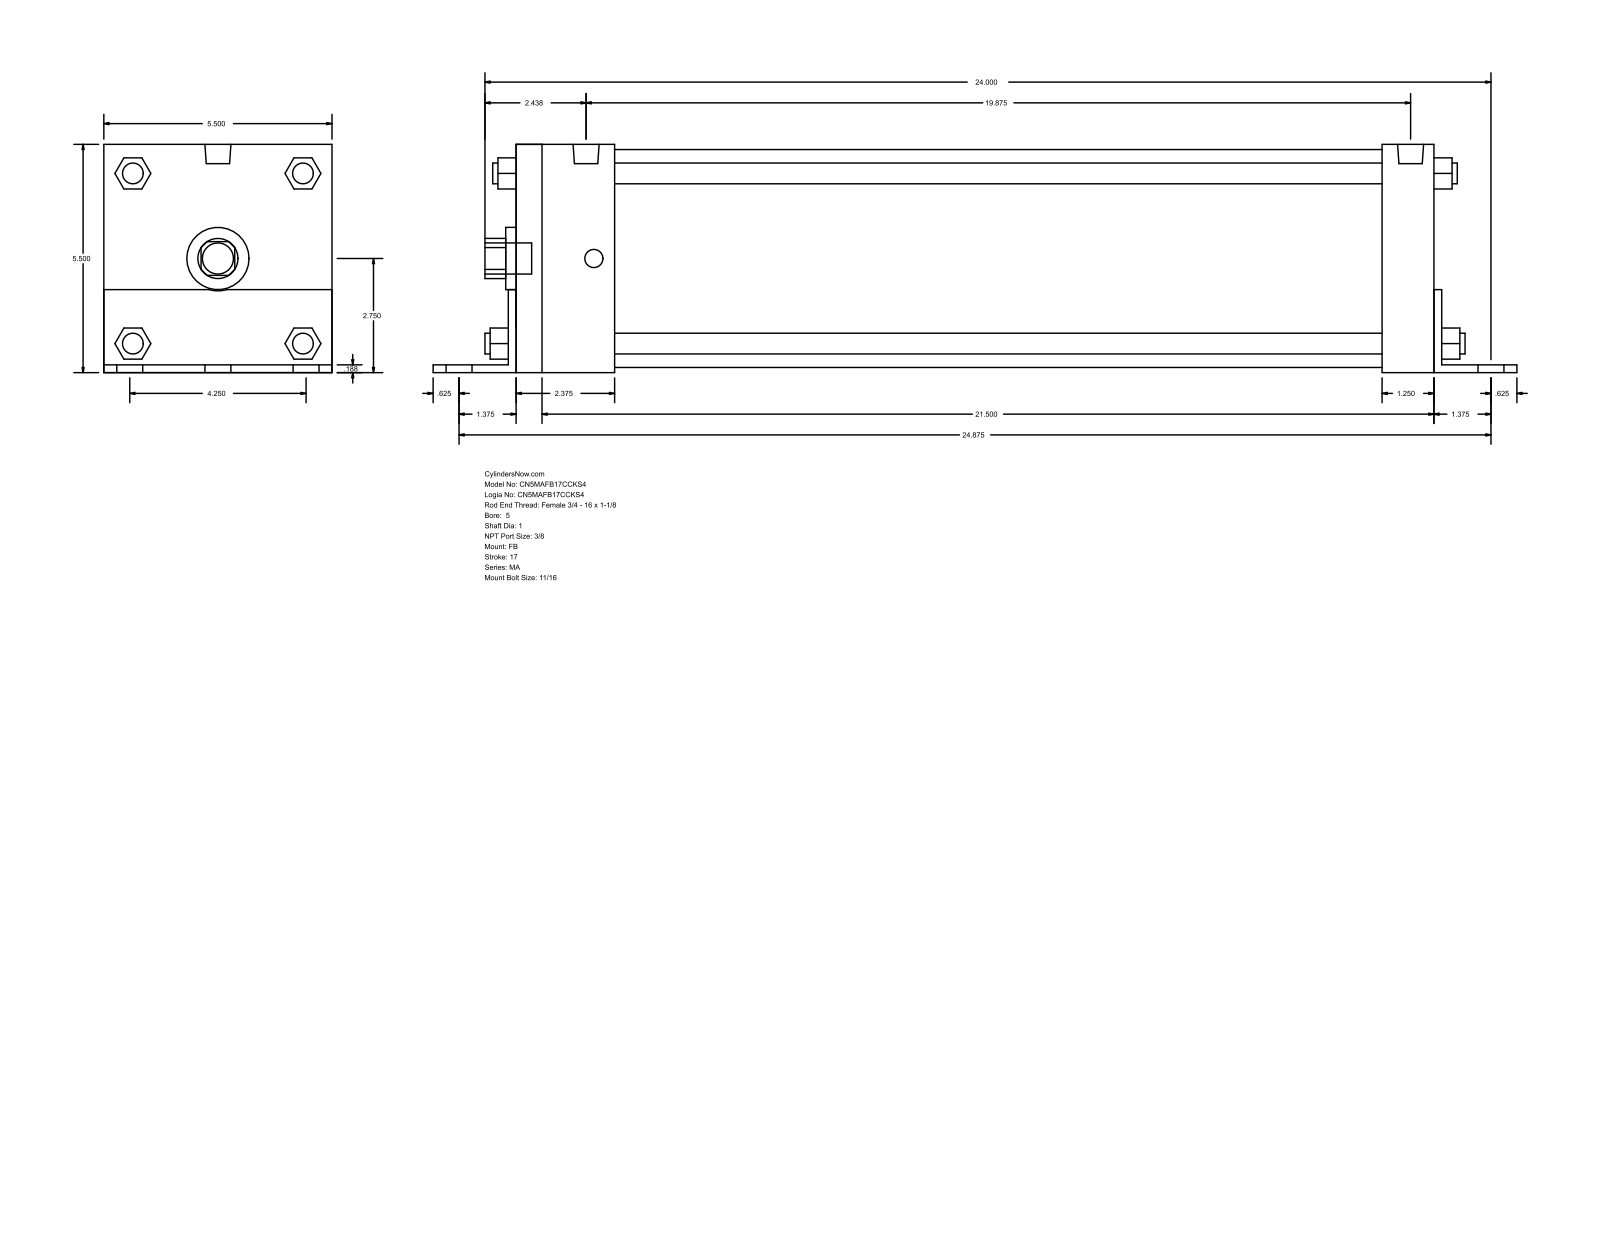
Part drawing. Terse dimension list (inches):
name: MA_FB__0500_1
written by: GSSL Pune (CONFIG_CONTROL_DESIGN)
unit: in
bodies: 0 solids, 140 faces (105 planar, 35 cylindrical, 0 other)
size: 26.125 × 5.502 × 5.5
holes: 1× ⌀1, 1× ⌀1.5, 1× ⌀5.25
bosses: 6× ⌀0.687, 4× ⌀0.5, 4× ⌀0.437, 2× ⌀0.627, 1× ⌀0.75
rounds: 1× R0.484, 1× R0.78
face distances: 5.5, 0.187, 5.502, 0.185, 5.315, 22.125, 0.188, 22.313, 22.312, 22.5
